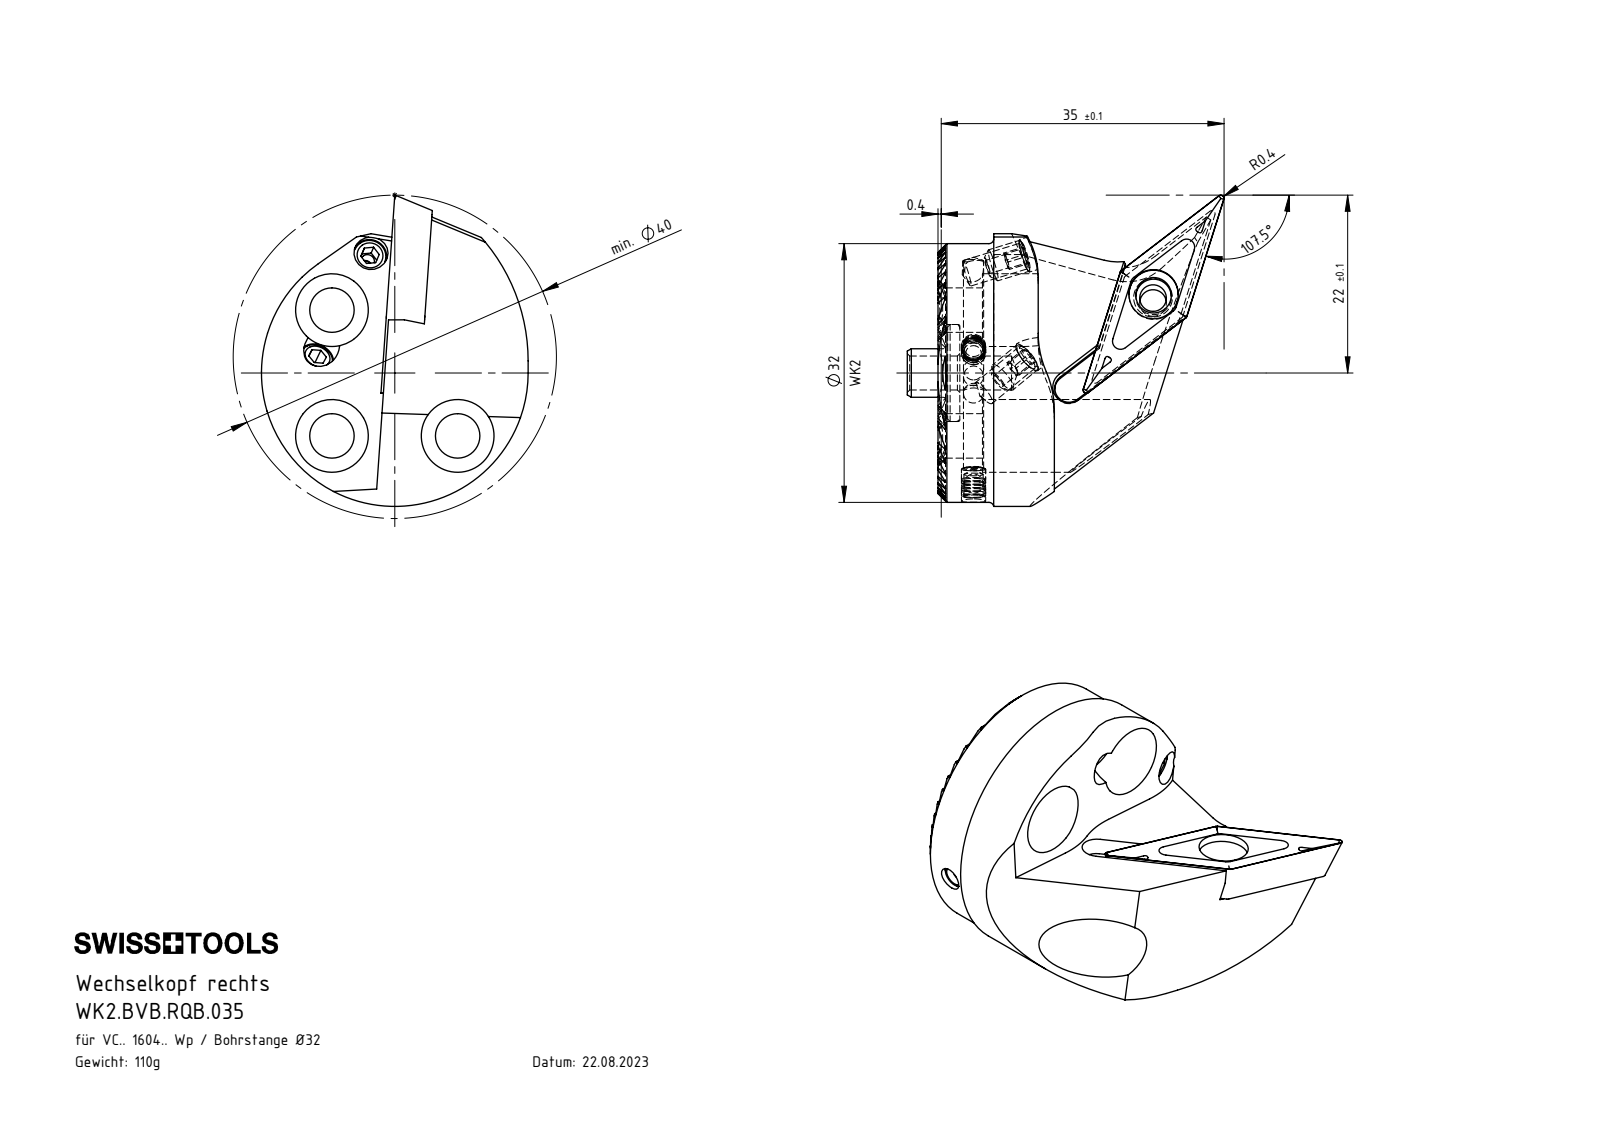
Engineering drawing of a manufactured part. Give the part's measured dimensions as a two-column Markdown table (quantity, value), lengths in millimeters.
| quantity | value |
| --- | --- |
| part name | VCMT160404; WK2-ER1.001.012_A_Fertigbearbeitung; WKX-ER1.004.005_A_PreviewCfg; WK2.BVB.RQB.035 (+2 more) |
| STEP written by | SolidWorks 2017 (AUTOMOTIVE_DESIGN) |
| units | millimeters |
| bodies | 9 solids, 361 faces (195 planar, 84 cylindrical, 82 other) |
| overall size | 39.2 × 38.5 × 33 |
| volume | 13 583 mm³ |
| surface area | 7 756 mm² |
| round holes (diameter × count) | 3.3 × 3, 4.2 × 3, 5.5 × 3, 9 × 3, 1.7 × 2, 2.38 × 2, 2.5 × 2, 3 × 2, 4.4 × 1, 6.1 × 1, 12 × 1 |
| round bosses / shafts (diameter × count) | 4 × 2, 3 × 2, 32 × 1, 6 × 1 |
| partial cylindrical surfaces (radius × count) | 0.12 × 22, 12 × 3, 1.75 × 1, 7 × 1, 16.5 × 1, 23 × 1 |
| main face-to-face distances | 1.3, 2.6, 3.9, 5.2, 6.5, 12.99, 11.69, 14.29, 7.8, 10.39 |
| hole center spacings | 11, 15.56, 22.01 |
